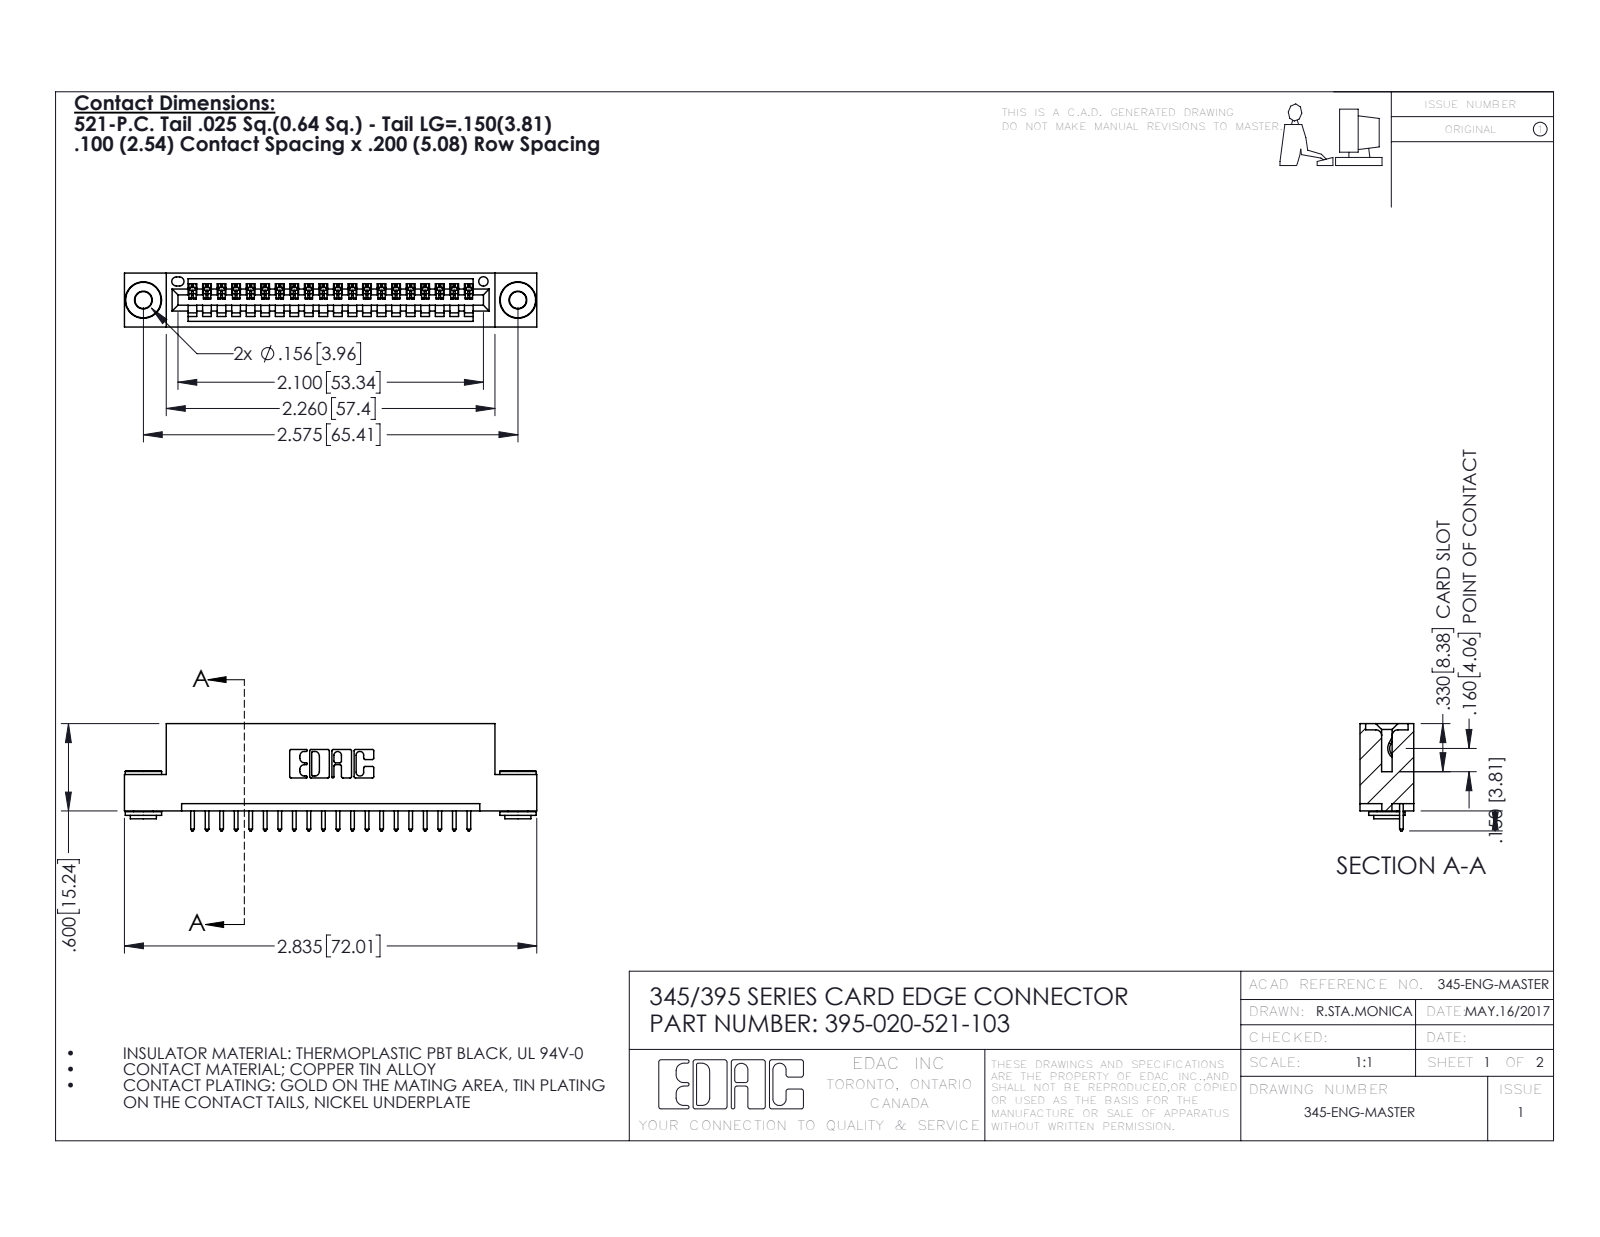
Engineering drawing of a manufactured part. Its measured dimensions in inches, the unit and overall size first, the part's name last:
Units: inches
Overall size (bounding box): 2.835 × 0.737 × 0.37
Round holes (diameter × count): ⌀0.116 ×2, ⌀0.156 ×2, ⌀0.064 ×1
Round bosses / shafts (diameter × count): ⌀0.25 ×2, ⌀0.18 ×2, ⌀0.136 ×2
Partial cylindrical surfaces — rounded edges, fillets, slot ends (radius × count): R0.006 ×40, R0.01 ×40, R0.01 ×22, R0.007 ×6, R0.031 ×6, R0.026 ×3, R0.031 ×2, R0.04 ×2
Main face-to-face distances: 0.072, 0.298, 0.2, 0.37, 0.025, 0.098, 0.272, 0.225, 0.149, 0.6
Hole centre spacings: 0.27, 2.341, 2.575
Volume: 0.404 in³ · Surface area: 13.16 in²
Bodies: 23 solids, 1324 faces (890 planar, 426 cylindrical, 8 other)
Part name (STEP PRODUCT): 345-250-002_345-250-002-102; 395-020-521-103; 345 Part_Flush Mounting Lugs - 0.156 Dia-TH; 345-292-001_345-293-121
STEP written by: SolidWorks 2016 (CONFIG_CONTROL_DESIGN)
